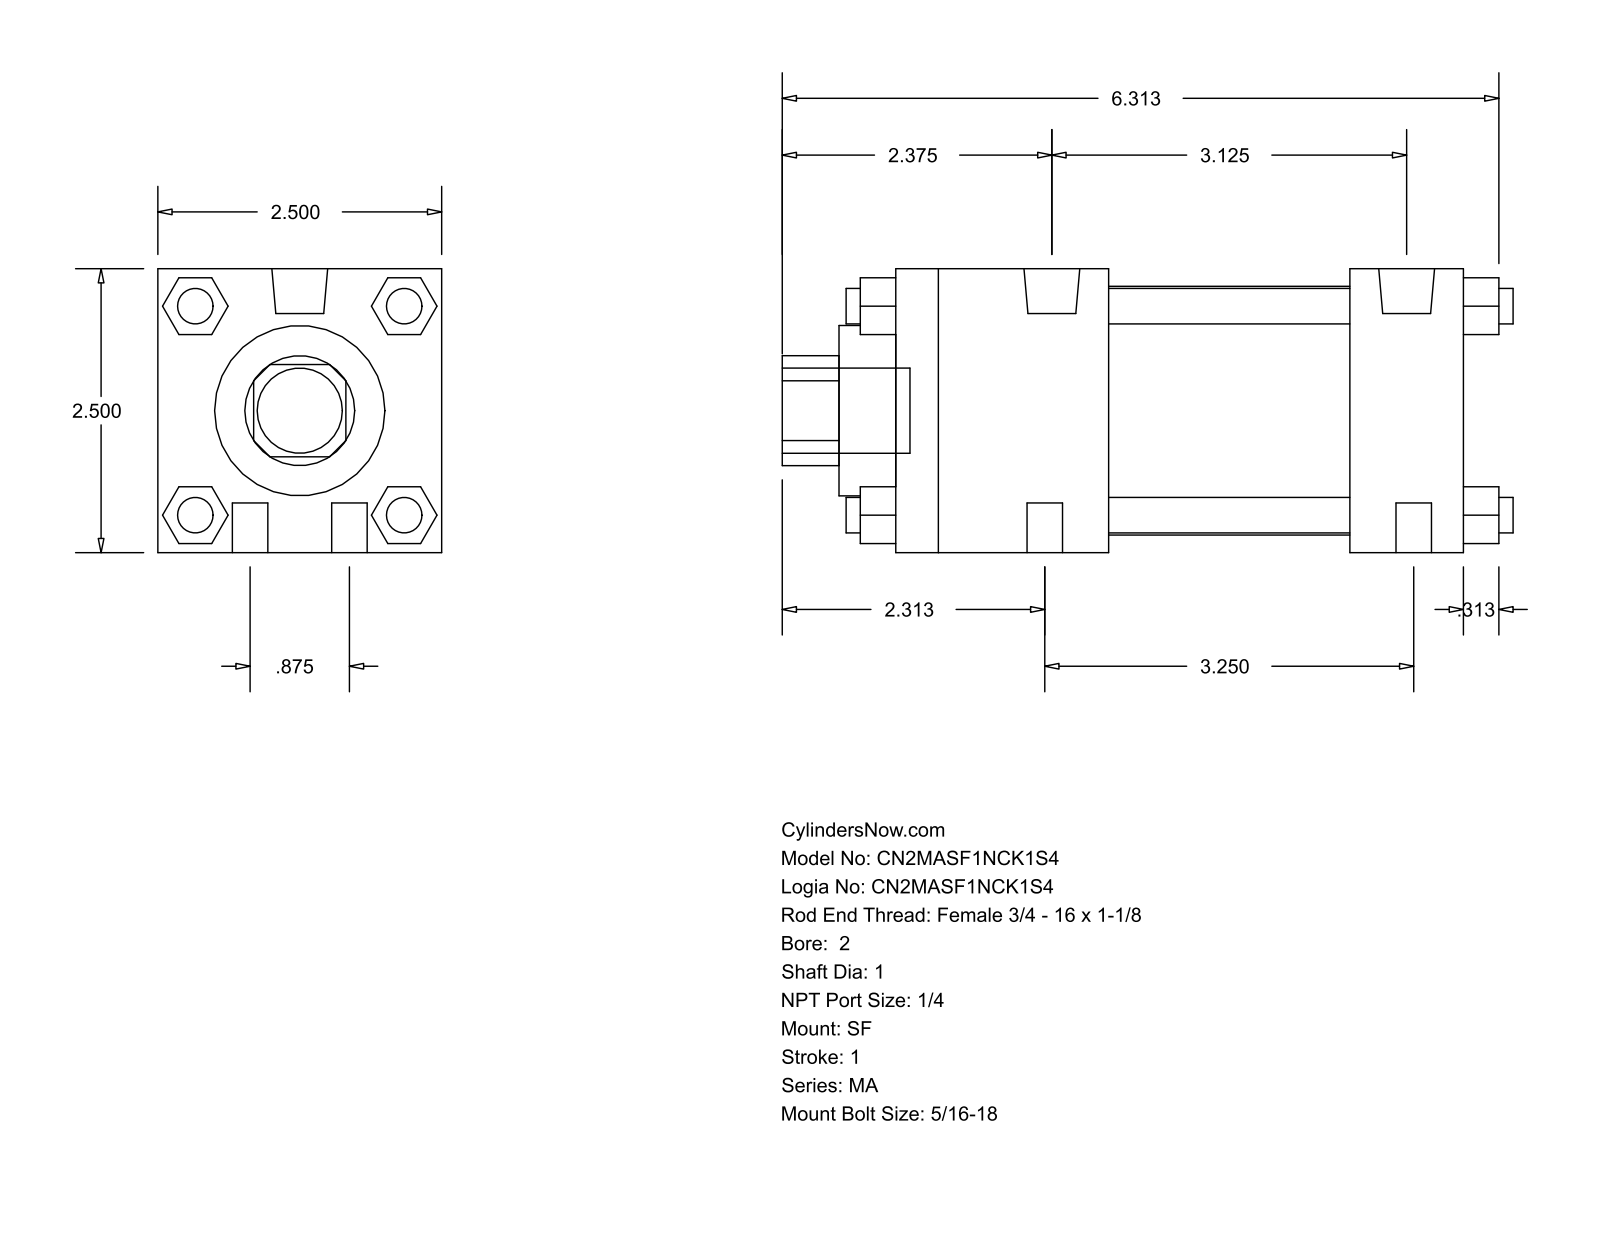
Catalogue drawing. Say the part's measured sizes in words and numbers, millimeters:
The part is named "MA_SF__0200_1". Its 3-D file was written by "GSSL Pune (CONFIG_CONTROL_DESIGN)". It is 0 solids with 124 faces: 94 planar, 30 cylindrical and 0 other. Overall it measures 163.51 by 63.5 by 63.5 millimeters. Round holes: 1 of diameter 25.4, 1 of diameter 38.1, 1 of diameter 55.63. Round bosses or shafts: 10 of diameter 7.94, 2 of diameter 12.49, 1 of diameter 19.05. Partial cylindrical surfaces (rounded edges, fillets, slot ends): 1 of radius 12.29. The main face-to-face distances are 63.5, 127, 12.7, 25.4, 101.6, 47.63, 53.97, 79.37, 23.37, 40.47.
